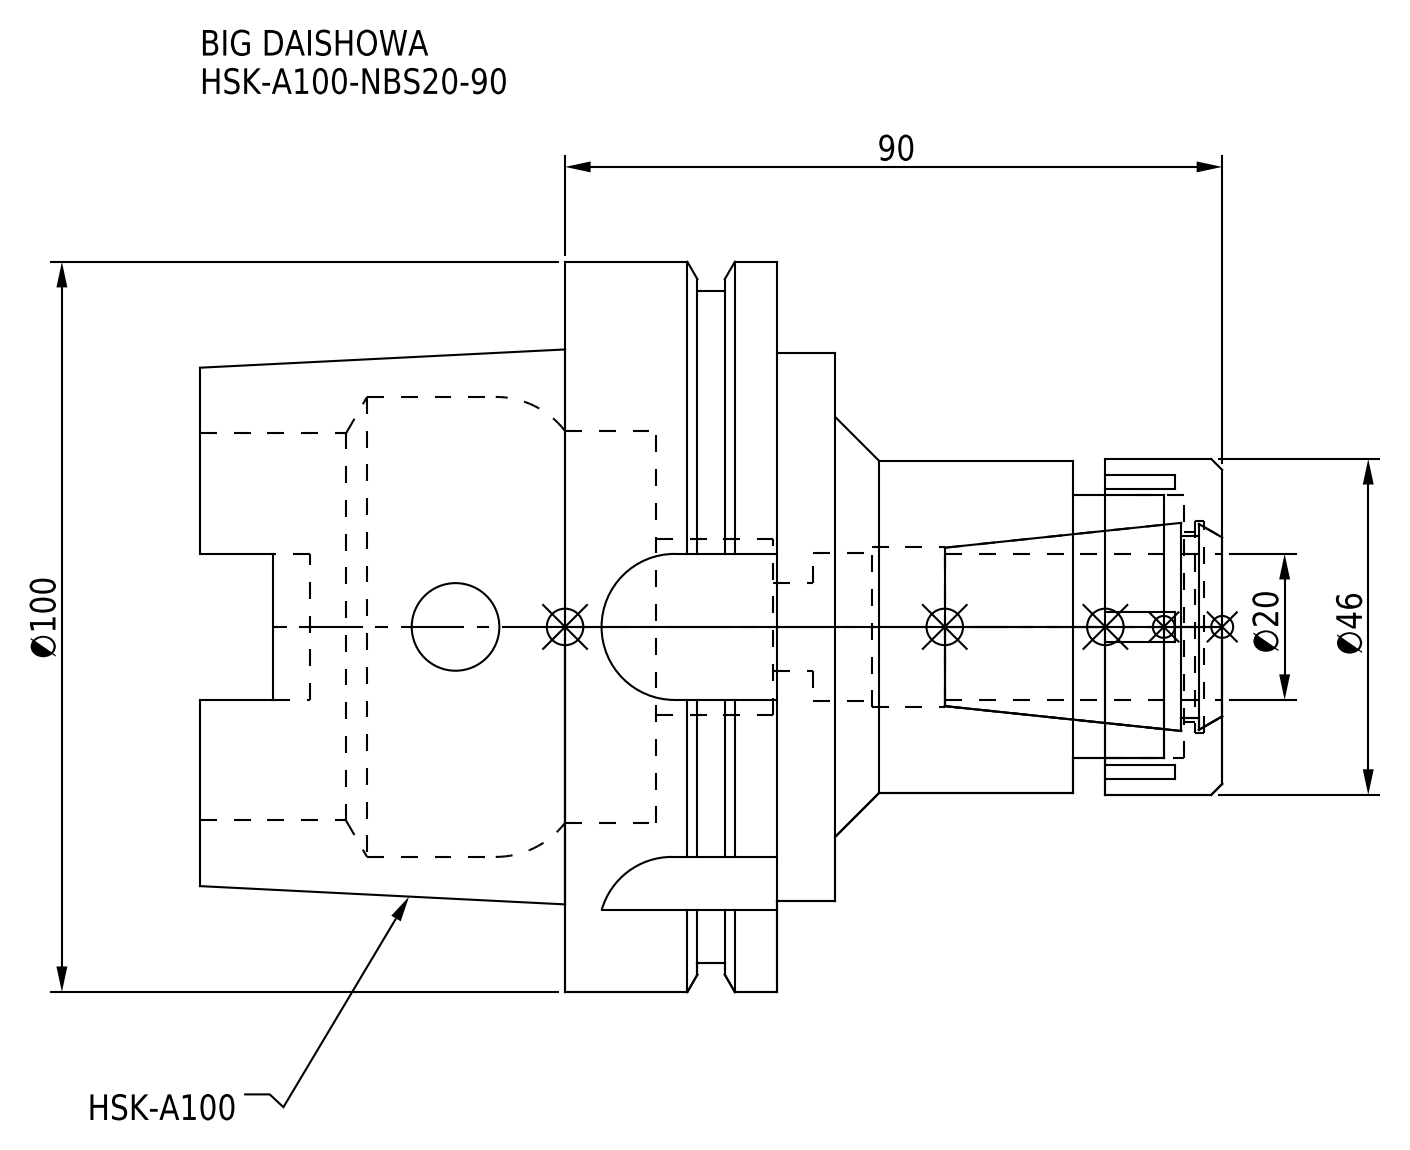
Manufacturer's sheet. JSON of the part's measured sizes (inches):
{"part_name": "HSK-A100-NBS20-90-FreeParts; DXF_TEMP_ASSY_ASM_4_ASM.stp; HA100NB20090-200_ASM.stp; HSK-A100-NBS20-90 (+3 more)", "step_written_by": "SolidWorks 2019 (CONFIG_CONTROL_DESIGN)", "units": "inches", "bodies": {"solids": 2, "faces": 138, "planar": 66, "cylindrical": 50, "other": 22}, "overall_size": [5.512, 3.937, 3.937], "volume_in3": 21.21, "surface_area_in2": 104.7, "round_holes": [[0.472, 2], [0.799, 1], [0.866, 1], [0.945, 1], [1.024, 1], [1.142, 1], [1.417, 1], [2.087, 1], [2.118, 1], [2.48, 1]], "round_bosses_or_shafts": [[3.937, 1], [3.622, 1], [2.953, 1], [1.811, 1], [1.791, 1]], "partial_cylinders_radius": [[0.192, 4], [0.394, 4]], "face_to_face_distances": [1.142, 0.315, 1.457, 0.967, 0.652, 0.49, 2.087, 3.425, 3.11, 2.459]}
